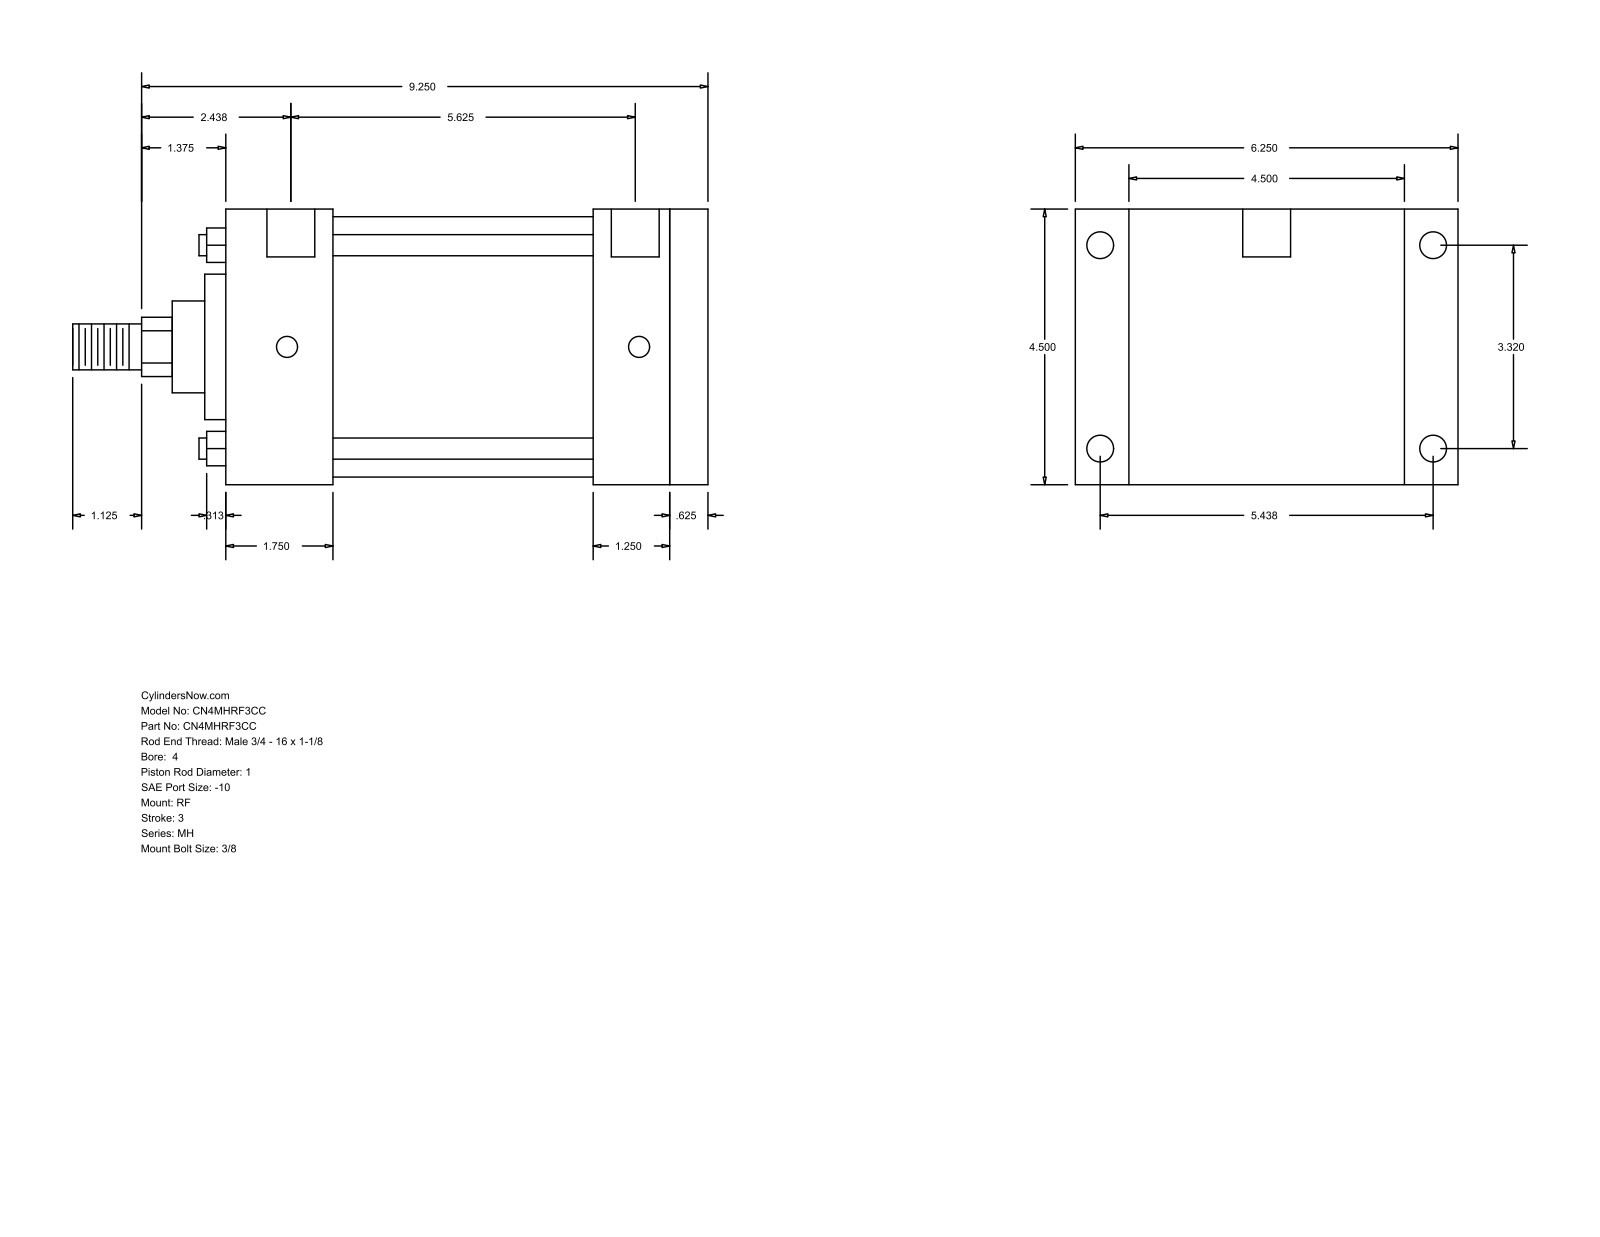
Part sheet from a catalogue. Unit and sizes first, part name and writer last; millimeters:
Units: millimetres
Overall size (bounding box): 263.52 × 158.75 × 114.3
Round holes (diameter × count): ⌀8.73 ×4, ⌀11.13 ×4, ⌀19.84 ×2
Round bosses / shafts (diameter × count): ⌀8.76 ×4, ⌀107.95 ×1, ⌀60.33 ×1, ⌀38.1 ×1, ⌀25.4 ×1, ⌀19.05 ×1
Partial cylindrical surfaces — rounded edges, fillets, slot ends (radius × count): R12.29 ×1
Main face-to-face distances: 114.3, 200.03, 184.15, 15.88, 47.63, 44.46, 139.69, 155.57, 152.4, 107.94
Hole centre spacings: 84.32, 138.12, 146.05, 161.82, 1.58, 1.59, 142.88, 144.46
Bodies: 0 solids, 94 faces (65 planar, 29 cylindrical, 0 other)
Part name (STEP PRODUCT): MH_RF__0400_1
STEP written by: GSSL Pune (CONFIG_CONTROL_DESIGN)
